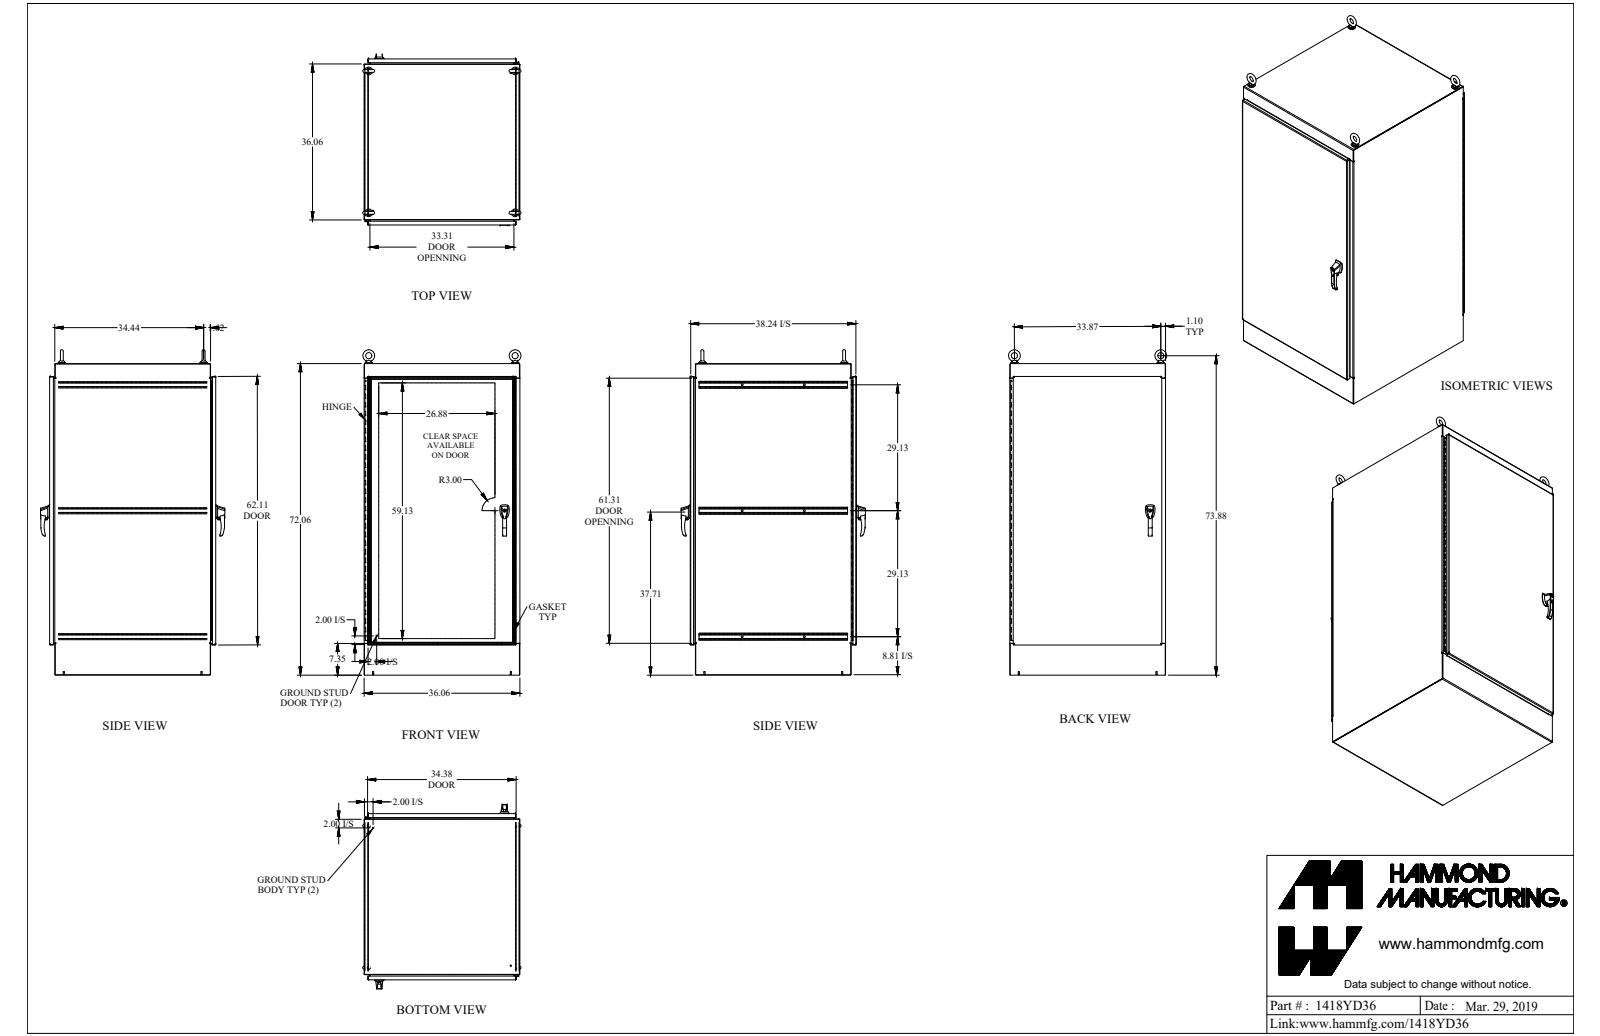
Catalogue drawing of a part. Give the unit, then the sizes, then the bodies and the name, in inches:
Units: inches
Overall size (bounding box): 75.713 × 42.664 × 37.118
Round holes (diameter × count): ⌀0.304 ×20, ⌀0.5 ×6, ⌀0.25 ×4, ⌀0.257 ×4, ⌀0.28 ×4, ⌀0.281 ×4, ⌀0.313 ×4, ⌀0.39 ×4, ⌀0.413 ×4, ⌀0.527 ×4, ⌀0.625 ×4, ⌀0.687 ×4
Round bosses / shafts (diameter × count): ⌀0.281 ×8, ⌀1.75 ×4, ⌀1.5 ×4, ⌀1.25 ×4, ⌀1 ×4, ⌀0.75 ×4, ⌀0.738 ×4, ⌀0.63 ×4
Partial cylindrical surfaces — rounded edges, fillets, slot ends (radius × count): R0.125 ×44, R0.043 ×42, R0.138 ×36, R0.018 ×32, R0.048 ×24, R0.143 ×24, R0.06 ×16, R0.318 ×14
Main face-to-face distances: 0.095, 35.965, 38.339, 35.87, 36.06, 71.965, 38.244, 38.434, 37.152, 1.187
Hole centre spacings: 6, 34.853, 12, 36.369, 18, 38.765, 24, 41.889
Volume: 1 541 in³ · Surface area: 32 389 in²
Bodies: 91 solids, 3188 faces (1386 planar, 1476 cylindrical, 326 other)
Part name (STEP PRODUCT): 1418YD36_Default
STEP written by: SolidWorks 2019 (CONFIG_CONTROL_DESIGN)
